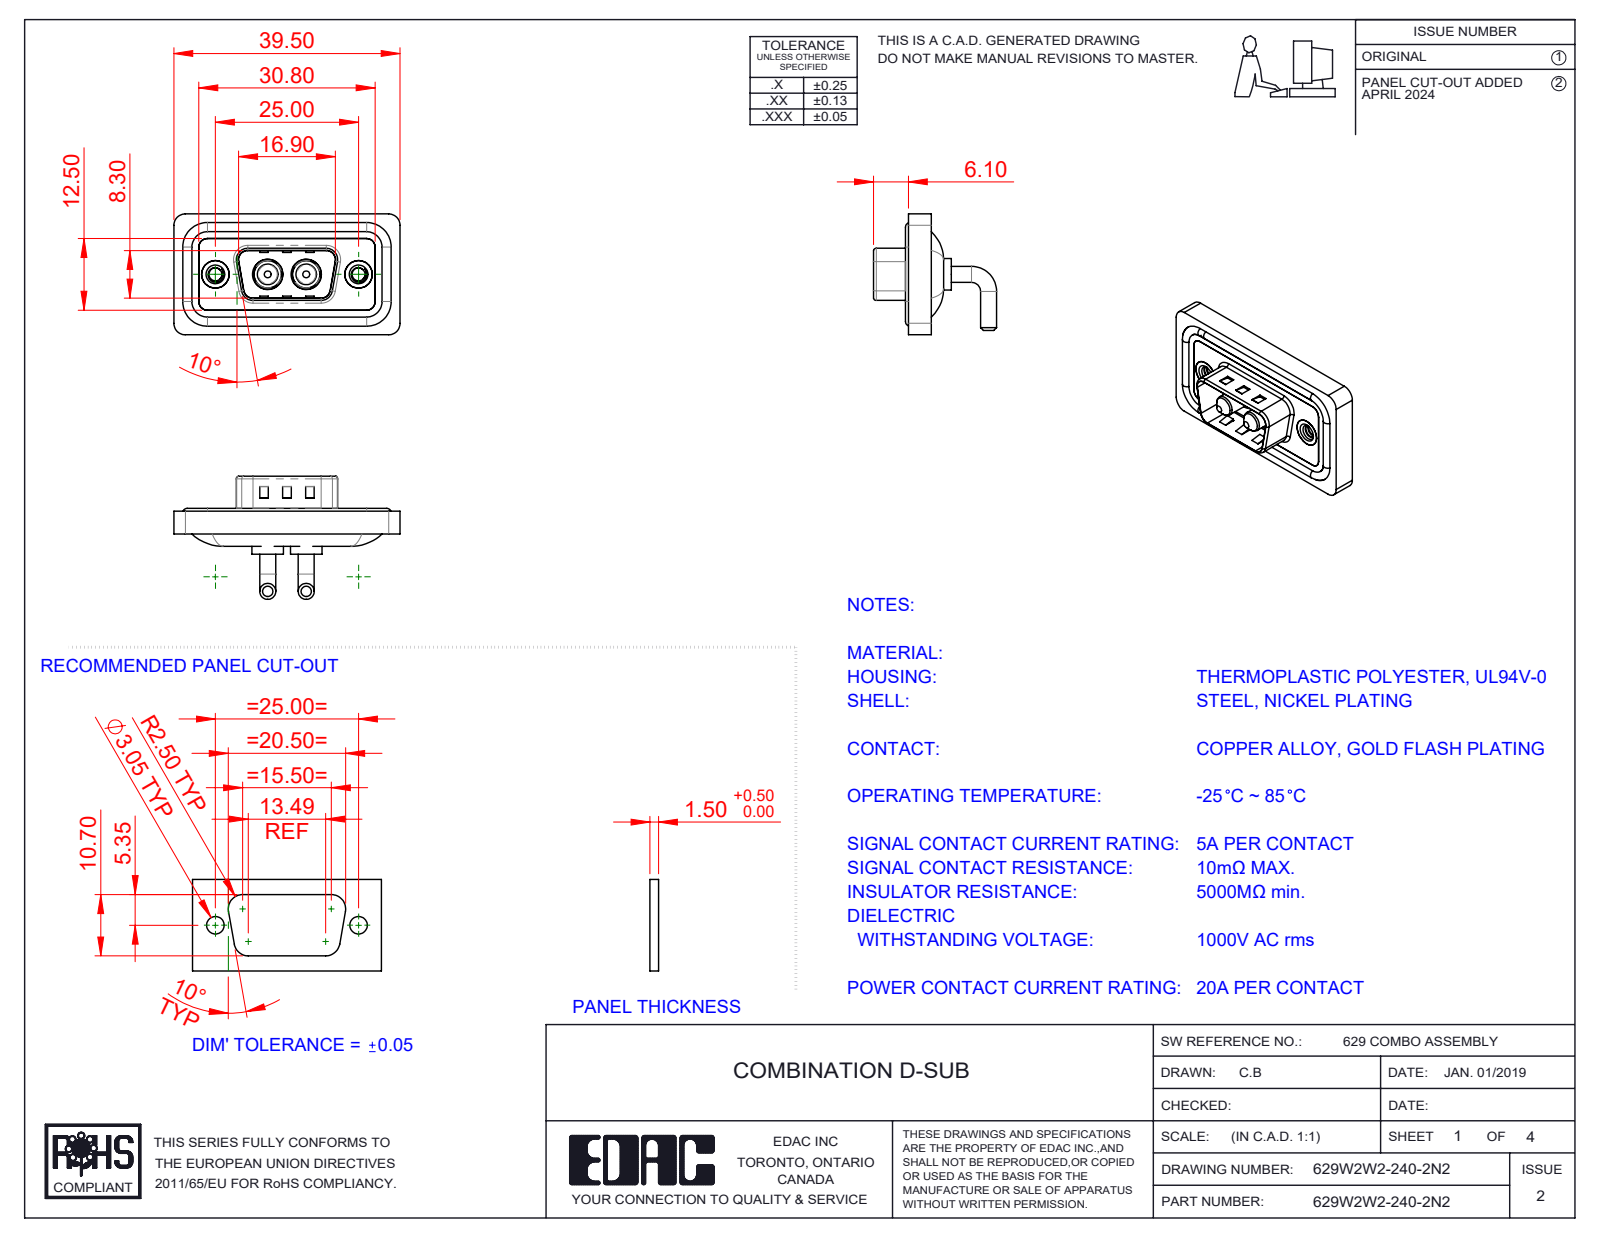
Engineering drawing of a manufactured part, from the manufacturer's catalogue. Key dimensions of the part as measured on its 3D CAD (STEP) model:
Part name (STEP PRODUCT): 629Combo Shell Front_09 Contacts; 629W2W2-240-2N2; 629Combo Shell Rear_09 Contacts; 629Combo Waterproof Housing_09 Contacts (+3 more)
STEP written by: SolidWorks 2023 (CONFIG_CONTROL_DESIGN)
Units: millimetres
Bodies: 11 solids, 497 faces (165 planar, 222 cylindrical, 110 other)
Overall size (bounding box): 39.5 × 21.5 × 21.1
Volume: 4 595 mm³ · Surface area: 7 168 mm²
Round holes (diameter × count): ⌀2.26 ×2, ⌀4 ×2, ⌀4.8 ×2, ⌀4.85 ×2, ⌀5 ×2, ⌀5.3 ×2
Round bosses / shafts (diameter × count): ⌀2.8 ×4, ⌀1.6 ×4, ⌀5.5 ×2, ⌀5.2 ×2, ⌀4.9 ×2, ⌀4.75 ×2, ⌀3.75 ×2, ⌀3.6 ×2
Partial cylindrical surfaces — rounded edges, fillets, slot ends (radius × count): R1.5 ×18, R2 ×18, R0.5 ×8, R1.6 ×8, R0.25 ×4, R0.6 ×4, R0.65 ×4, R0.9 ×4
Main face-to-face distances: 0.4, 2.9, 1.1, 0.8, 2.1, 2.5, 3.1, 1.6, 4.5, 1.5
Hole centre spacings: 9.14, 15.86, 6.72, 25
